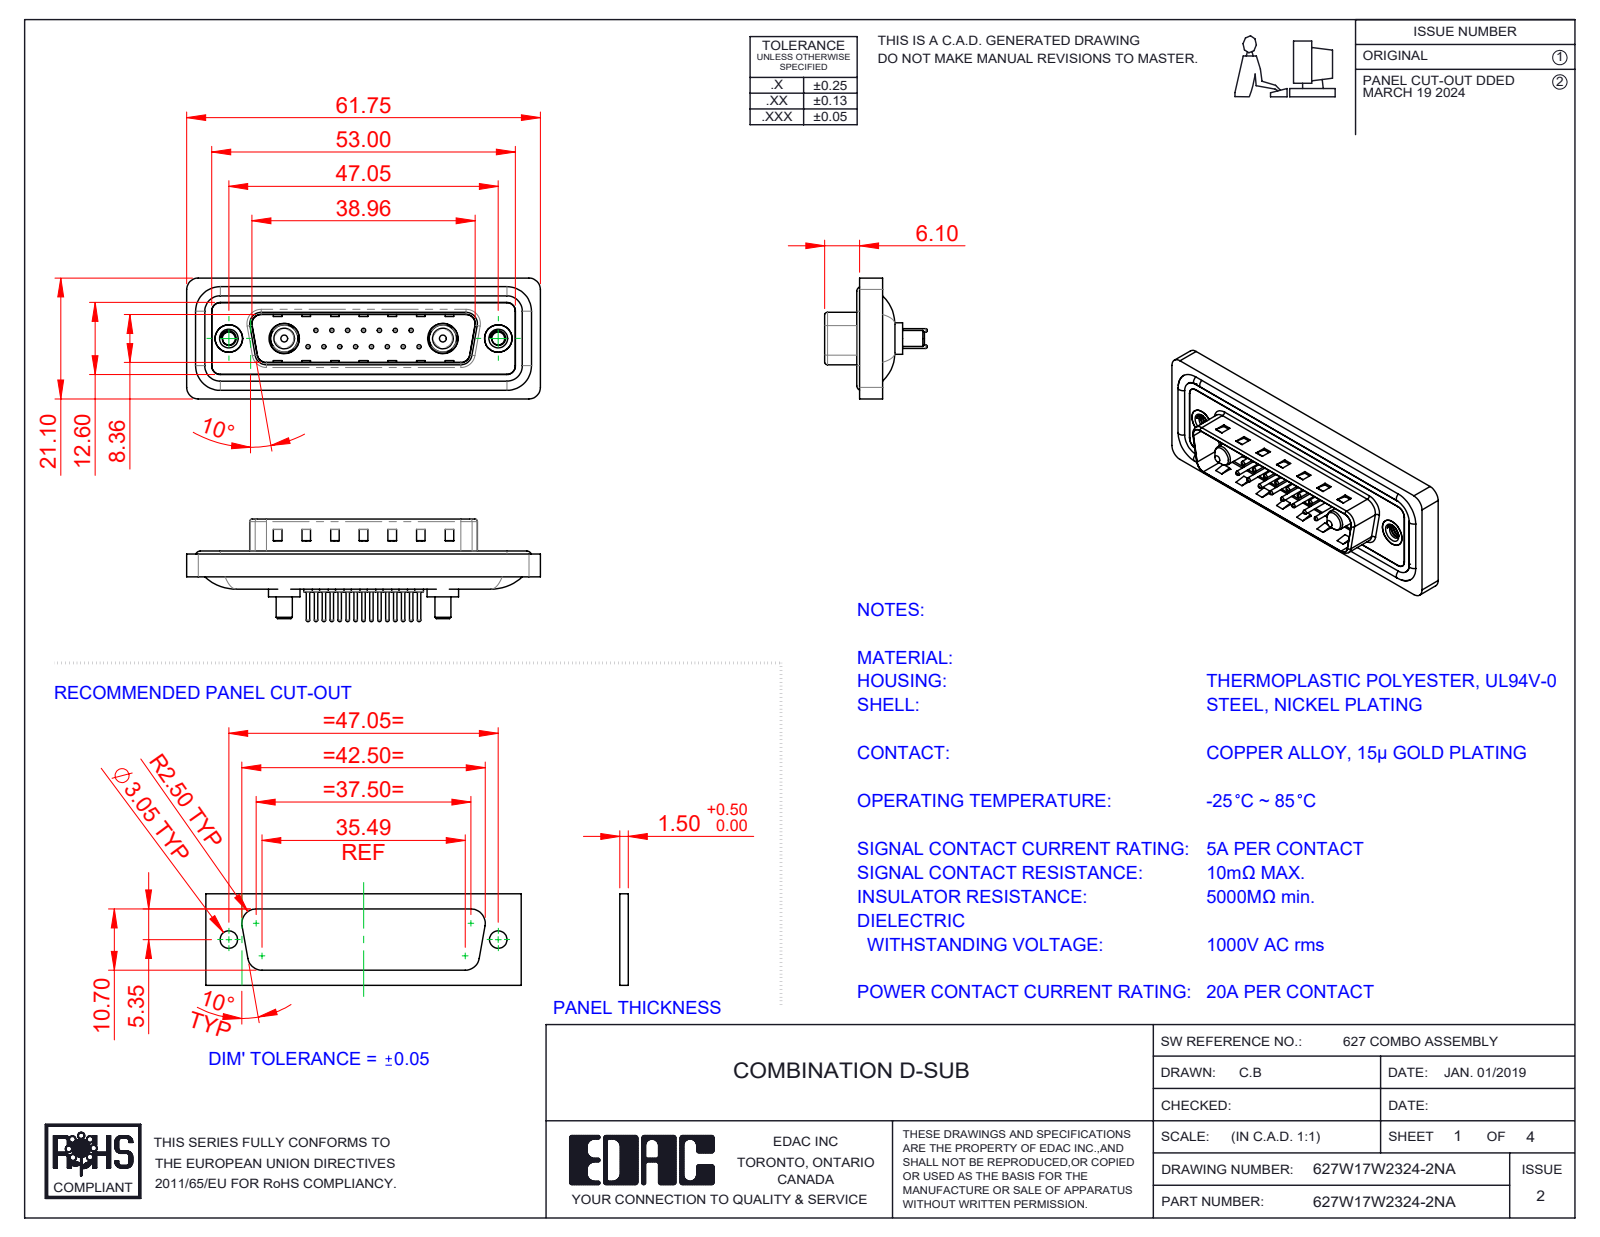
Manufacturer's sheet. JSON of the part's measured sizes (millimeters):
{"part_name": "627Combo Waterproof Housing_25 Contacts; Power Pin_20A S; 627Combo Threaded Rivet_A; 627Combo Shell Front_25 Contacts (+5 more)", "step_written_by": "SolidWorks 2023 (CONFIG_CONTROL_DESIGN)", "units": "millimeters", "bodies": {"solids": 26, "faces": 1114, "planar": 334, "cylindrical": 438, "other": 342}, "overall_size": [61.75, 21.1, 17.9], "volume_mm3": 7268, "surface_area_mm2": 11912, "round_holes": [[0.75, 15], [1.6, 15], [2, 15], [2.26, 2], [4, 2], [4.8, 2], [4.85, 2], [5, 2], [5.3, 2]], "round_bosses_or_shafts": [[1.5, 15], [0.6, 15], [1.6, 4], [5.5, 2], [5.2, 2], [4.9, 2], [4.75, 2], [3.75, 2]], "partial_cylinders_radius": [[1.5, 22], [2, 18], [0.5, 8], [1.6, 8], [0.25, 4], [0.6, 4], [0.65, 4], [0.9, 4]], "face_to_face_distances": [0.4, 1.5, 1.1, 1.6, 0.5, 3.1, 2.9, 0.82, 9.58, 4.1], "hole_center_spacings": [3.16, 2.77, 5.54, 8.31, 5.04, 7.49, 11.08, 5.03]}
